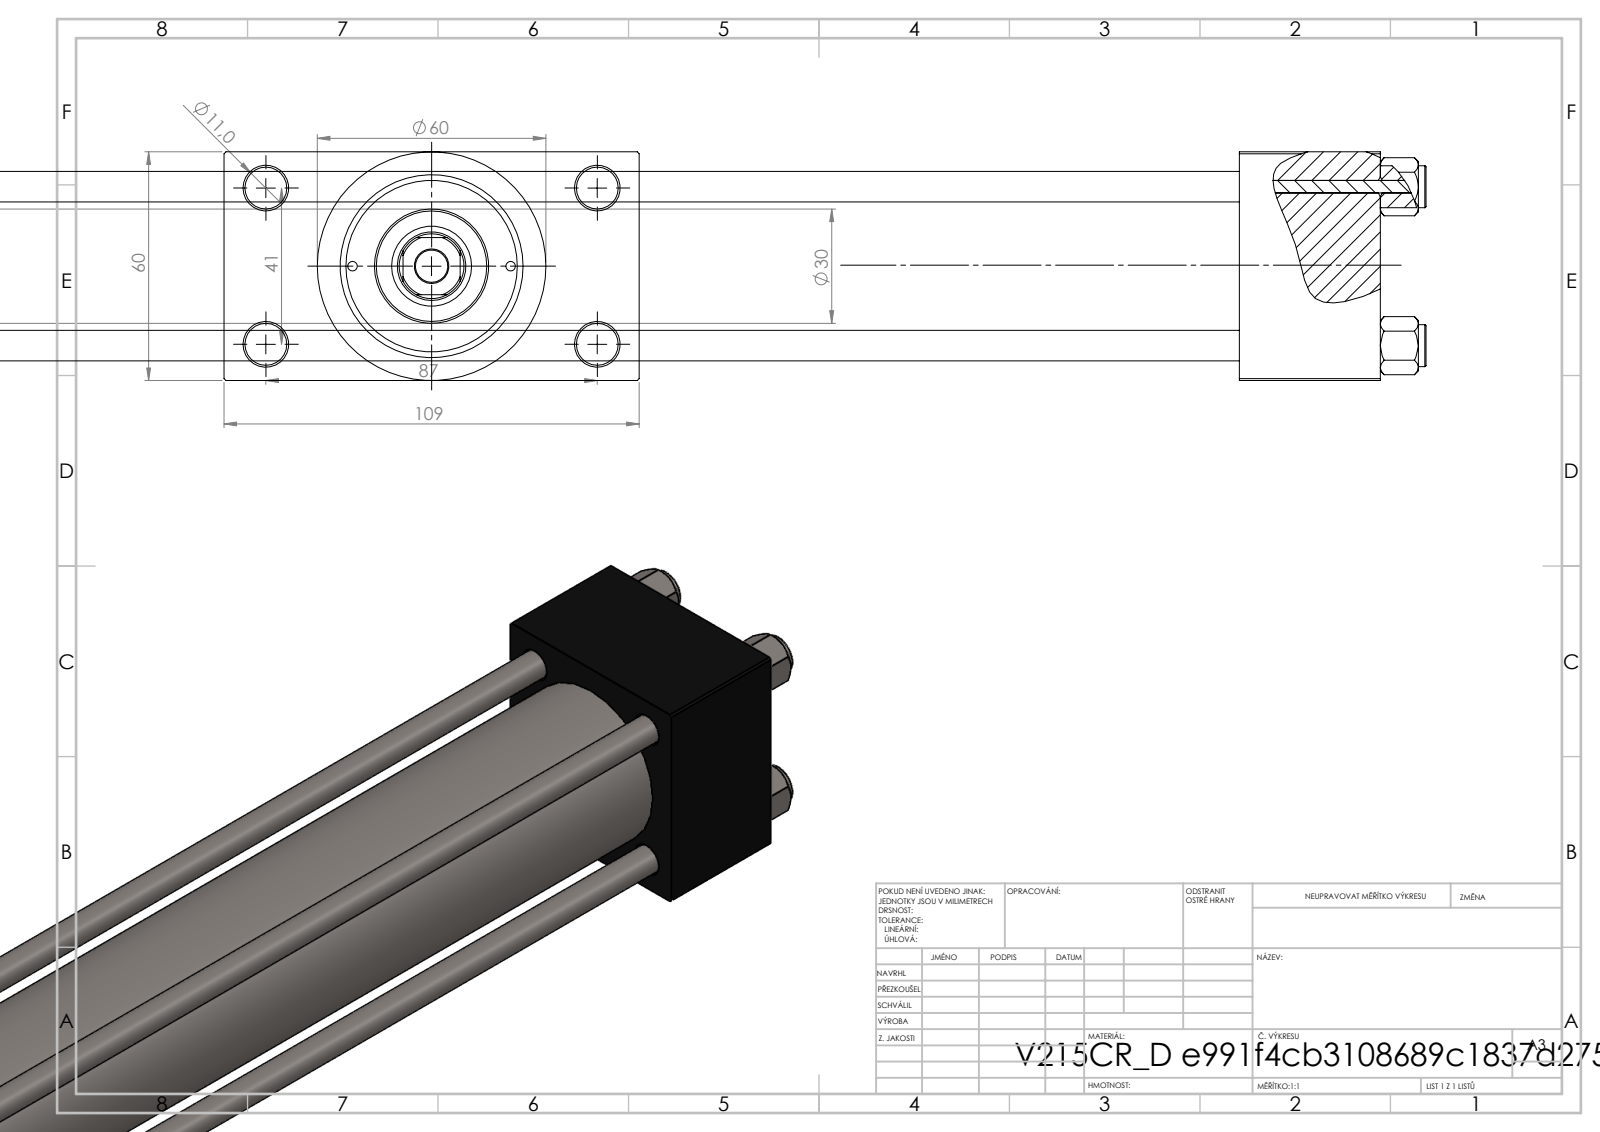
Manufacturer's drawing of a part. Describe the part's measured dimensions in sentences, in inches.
The part is named "V215CR_D_TYCINKA; V215CR_D_Body; V215CR_VCP_D; V215_VC_A (+1 more)". Its 3-D file was written by "SolidWorks 2019 (CONFIG_CONTROL_DESIGN)". It is 11 solids with 1112 faces: 500 planar, 92 cylindrical and 520 other. Overall it measures 20.276 by 4.291 by 2.362 inches. Its volume is 48.6 cubic inches and its surface area 408.4 square inches. Round holes: 4 of diameter 0.315, 4 of diameter 0.433, 2 of diameter 0.098, 2 of diameter 0.276, 2 of diameter 0.656, 2 of diameter 0.945, 1 of diameter 0.335, 1 of diameter 0.709, 1 of diameter 0.827, 1 of diameter 1.22, 1 of diameter 1.575, 1 of diameter 1.772. Round bosses or shafts: 4 of diameter 0.433, 1 of diameter 2.362, 1 of diameter 1.811, 1 of diameter 1.181. Partial cylindrical surfaces (rounded edges, fillets, slot ends): 1 of radius 0.335. The main face-to-face distances are 2.362, 15.276, 0.965, 3.327, 1.457, 16.732, 18.425, 16.969, 1.693, 17.116. The hole center spacings are 0.821, 0.892, 1.161, 1.206, 1.642, 1.832, 1.856, 1.893.
